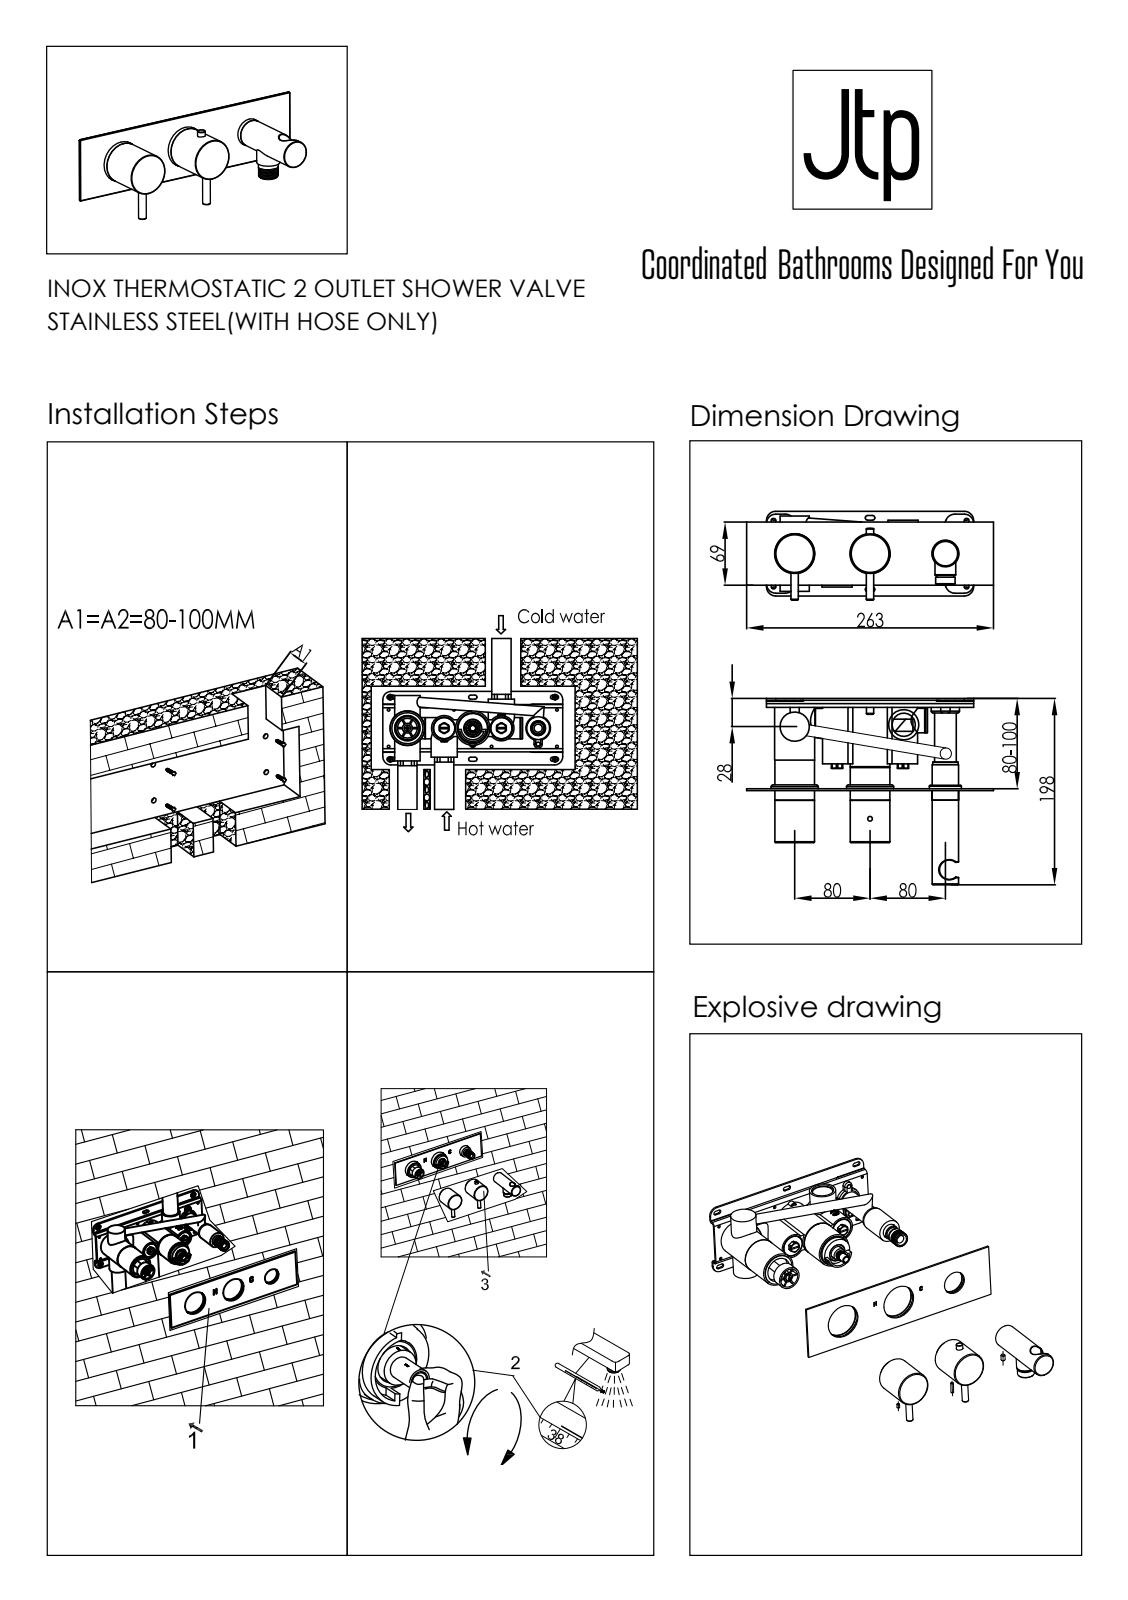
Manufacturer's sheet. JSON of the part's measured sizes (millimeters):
{"part_name": "5868", "step_written_by": "PRO/ENGINEER BY PARAMETRIC TECHNOLOGY CORPORATION, 2012130 (CONFIG_CONTROL_DESIGN)", "units": "millimeters", "bodies": {"solids": 4, "faces": 122, "planar": 22, "cylindrical": 51, "other": 49}, "overall_size": [6680.2, 2286, 2171.7], "volume_mm3": 3961000000, "surface_area_mm2": 41600000, "round_holes": [[1079.5, 2], [723.9, 1]], "round_bosses_or_shafts": [[203.2, 3], [1066.8, 2], [711.2, 1], [609.6, 1], [523.2, 1]], "partial_cylinders_radius": [[12.7, 8], [25.4, 4]], "face_to_face_distances": [50.8, 127, 76.2, 1397, 1320.8, 1270, 2286, 2209.8, 2159, 889], "hole_center_spacings": [2032, 4064]}
